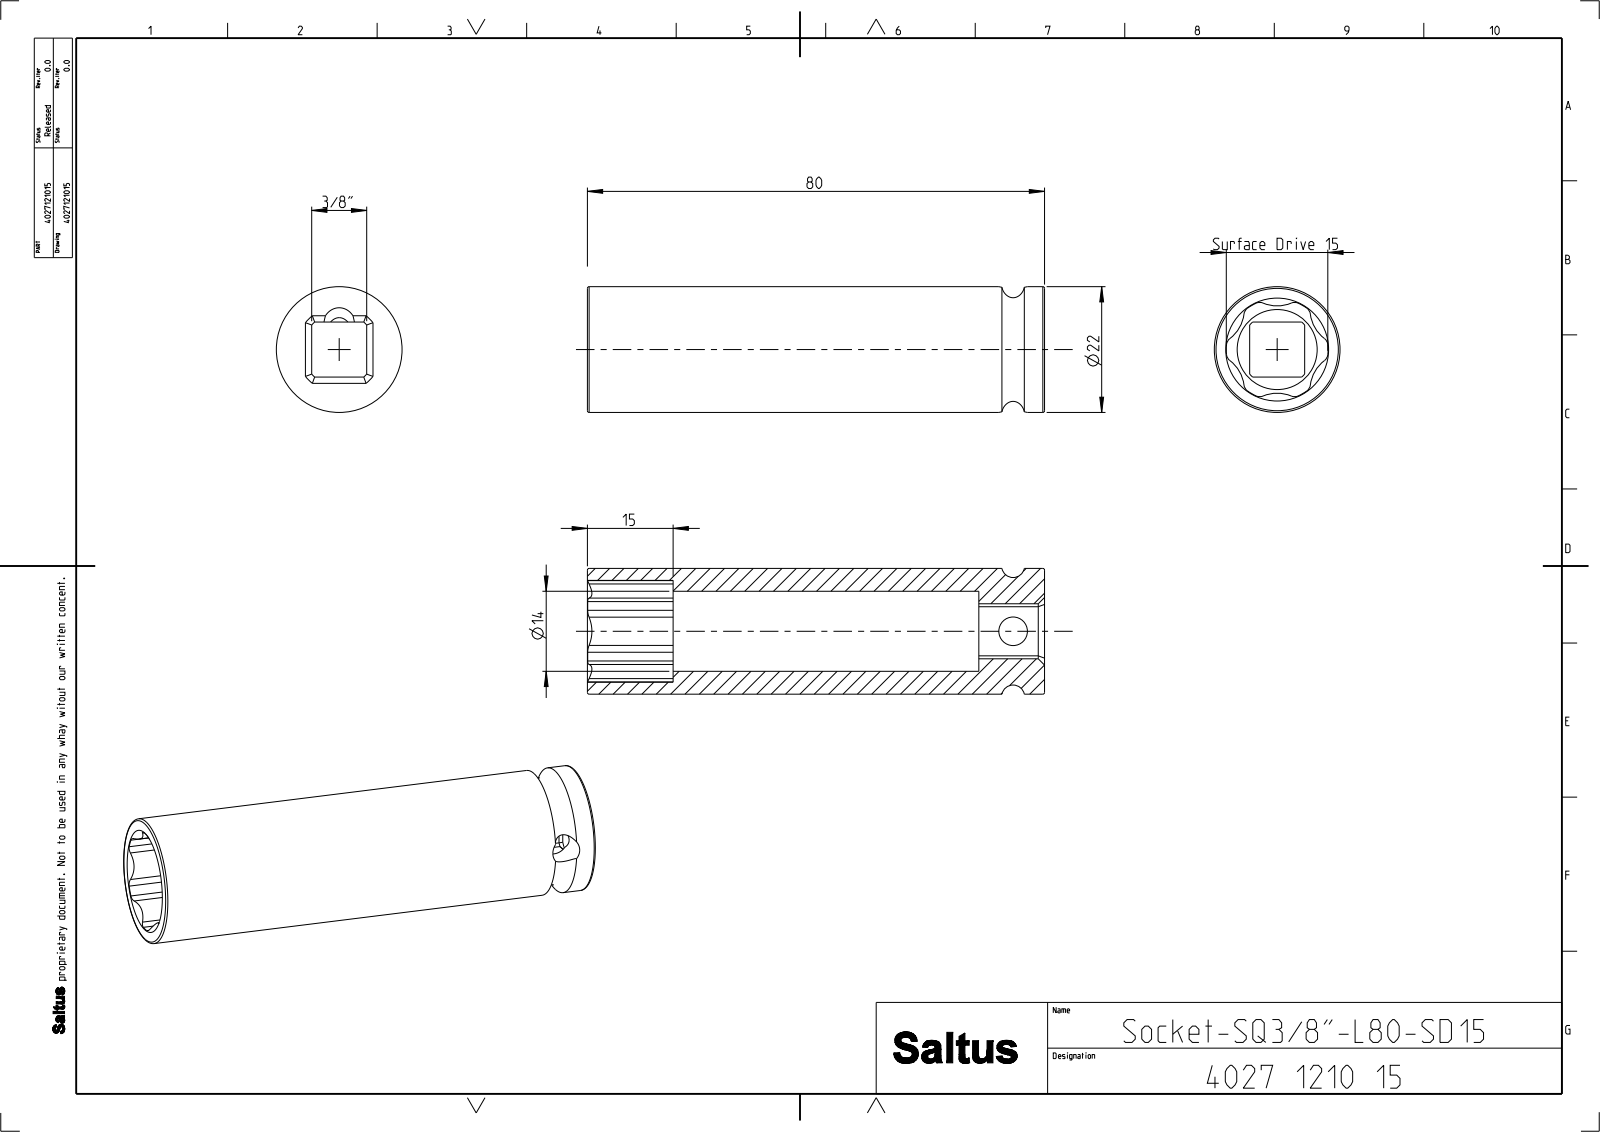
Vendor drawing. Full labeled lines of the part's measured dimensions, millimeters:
Part name (STEP PRODUCT): 4027121015
STEP written by: CREO PARAMETRIC BY PTC INC, 2022414 (CONFIG_CONTROL_DESIGN)
Units: millimetres
Bodies: 1 solid, 64 faces (13 planar, 39 cylindrical, 12 other)
Overall size (bounding box): 80 × 22 × 22
Volume: 17 297 mm³ · Surface area: 9 815 mm²
Round holes (diameter × count): ⌀5 ×1, ⌀14 ×1
Round bosses / shafts (diameter × count): ⌀22 ×1
Partial cylindrical surfaces — rounded edges, fillets, slot ends (radius × count): R1.5 ×12, R6.4 ×6, R3 ×1, R6.45 ×1, R8.9 ×1
Main face-to-face distances: 9.62, 80, 65, 15, 11.5, 53.5, 68.5
